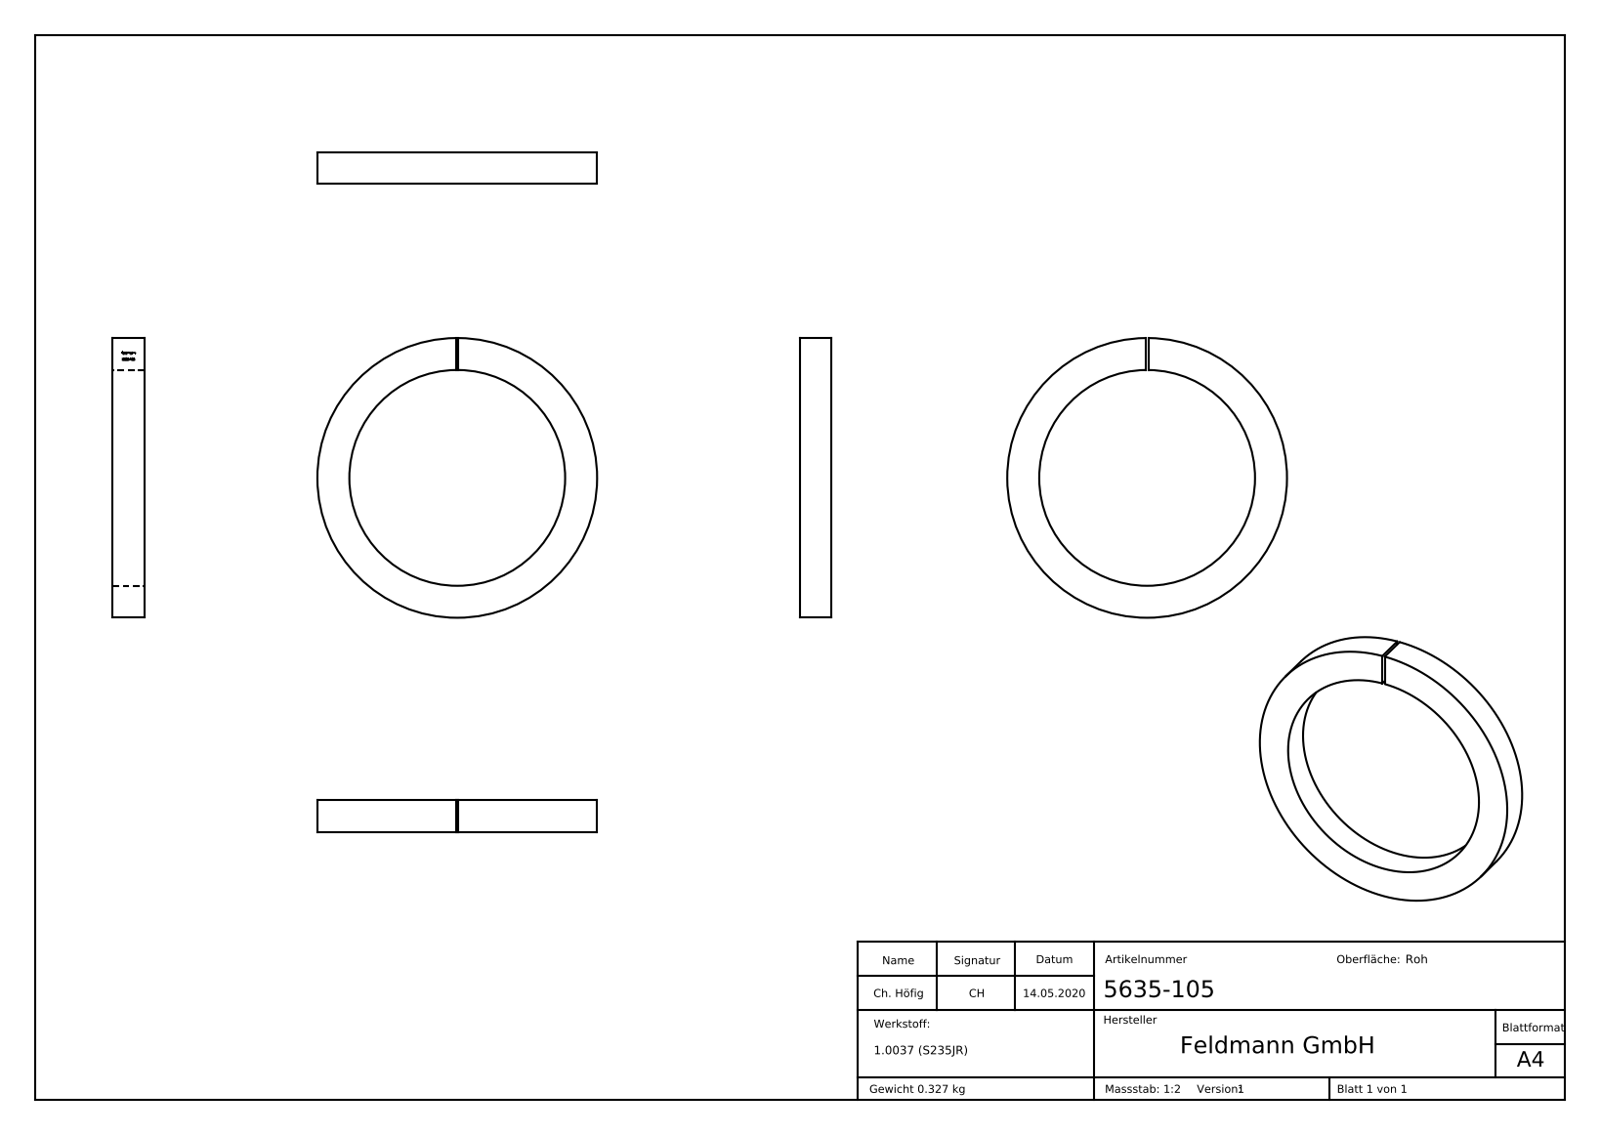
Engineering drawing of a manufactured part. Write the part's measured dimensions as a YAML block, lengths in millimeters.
part_name: "5635-105"
step_written_by: "SolidWorks 2015 (CONFIG_CONTROL_DESIGN)"
units: millimeters
bodies: {solids: 1, faces: 219, planar: 113, cylindrical: 2, other: 104}
overall_size: [105, 105, 12]
volume: 41928
surface_area: 14269
round_holes:
  - {diameter: 81, count: 1}
round_bosses_or_shafts:
  - {diameter: 105, count: 1}
face_to_face_distances: [12, 1, 1.1, 1.78, 2.12, 0.83, 2.45, 0.99, 2.77, 1.21]
